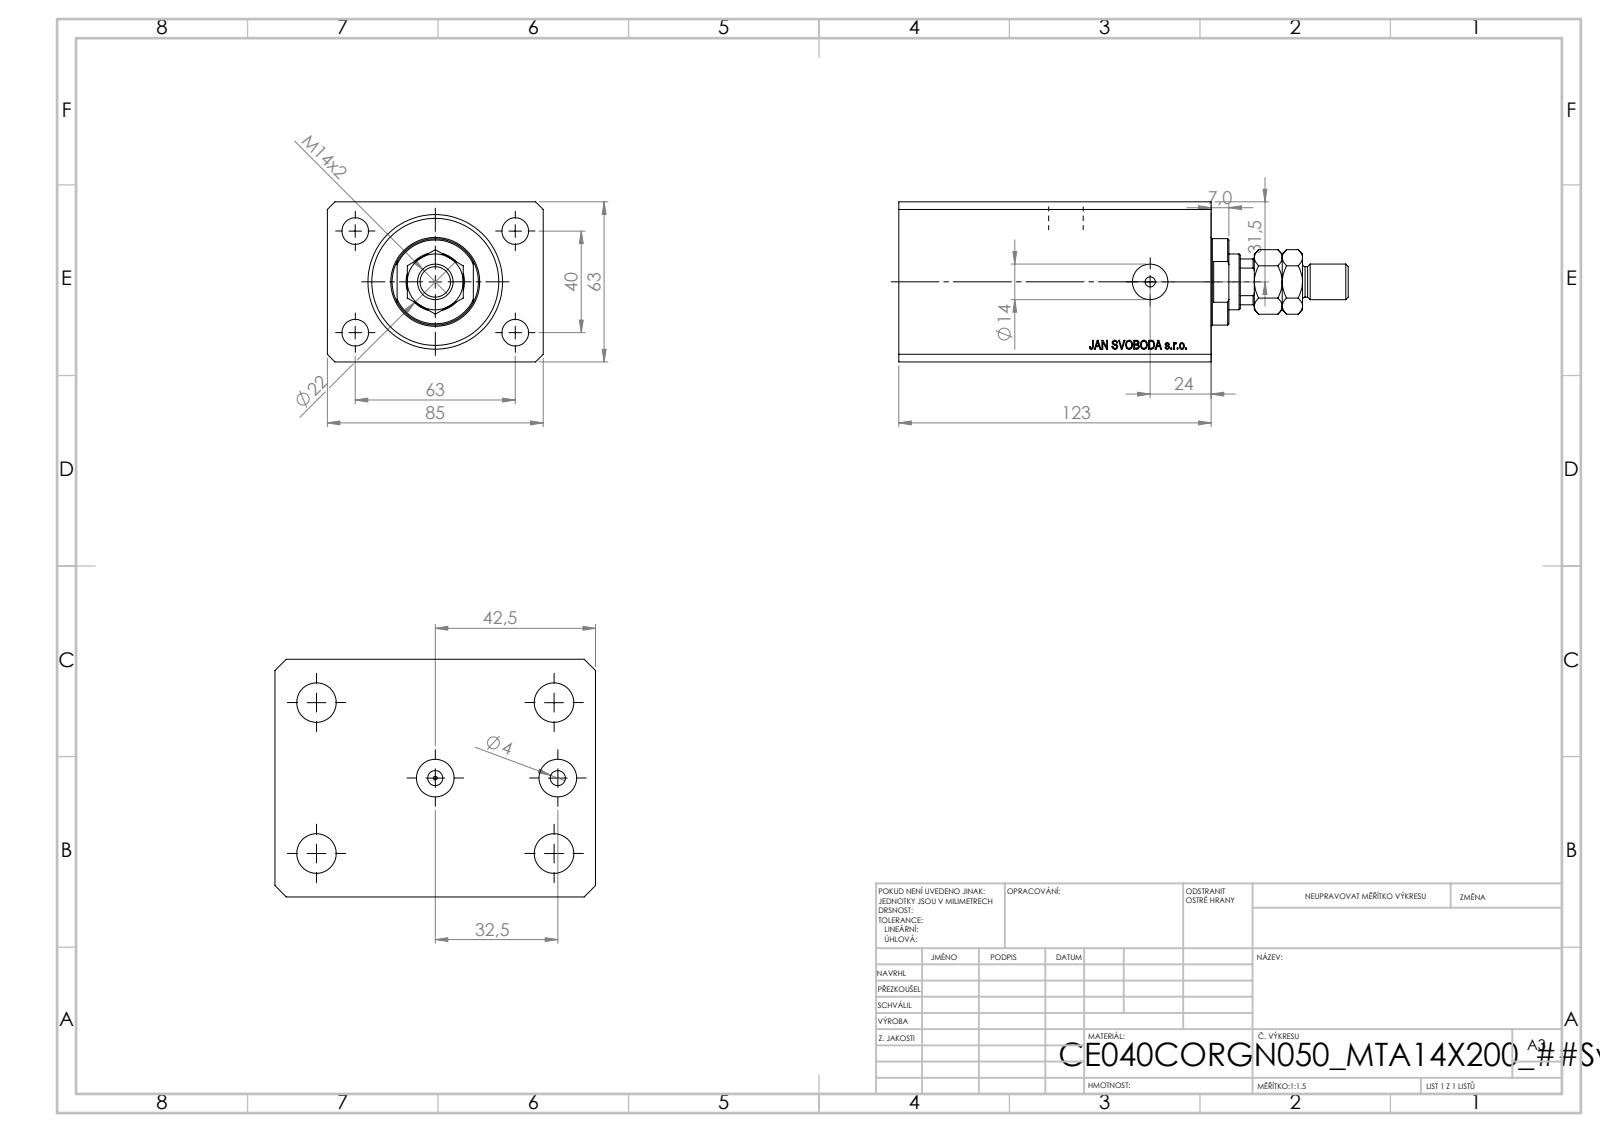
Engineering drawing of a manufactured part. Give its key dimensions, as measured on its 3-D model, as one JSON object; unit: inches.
{"part_name": "V250CE_C_Body; V250CE_VC_C; MTA; V250CE_C_VCP", "step_written_by": "SolidWorks 2019 (CONFIG_CONTROL_DESIGN)", "units": "inches", "bodies": {"solids": 4, "faces": 917, "planar": 443, "cylindrical": 50, "other": 424}, "overall_size": [6.969, 3.346, 2.48], "volume_in3": 35.61, "surface_area_in2": 163.8, "round_holes": [[0.157, 4], [0.413, 4], [0.394, 2], [0.551, 2], [0.049, 1], [0.492, 1], [0.866, 1], [1.575, 1], [2.087, 1]], "round_bosses_or_shafts": [[1.339, 1], [0.551, 1], [0.472, 1]], "partial_cylinders_radius": [[0.413, 1]], "face_to_face_distances": [2.48, 3.346, 4.843, 0.669, 4.173, 0.449, 3.724, 4.394, 3.953, 2.205], "hole_center_spacings": [1.469, 0.788, 1.575, 2.48, 2.64, 2.938, 1.28, 2.953]}
